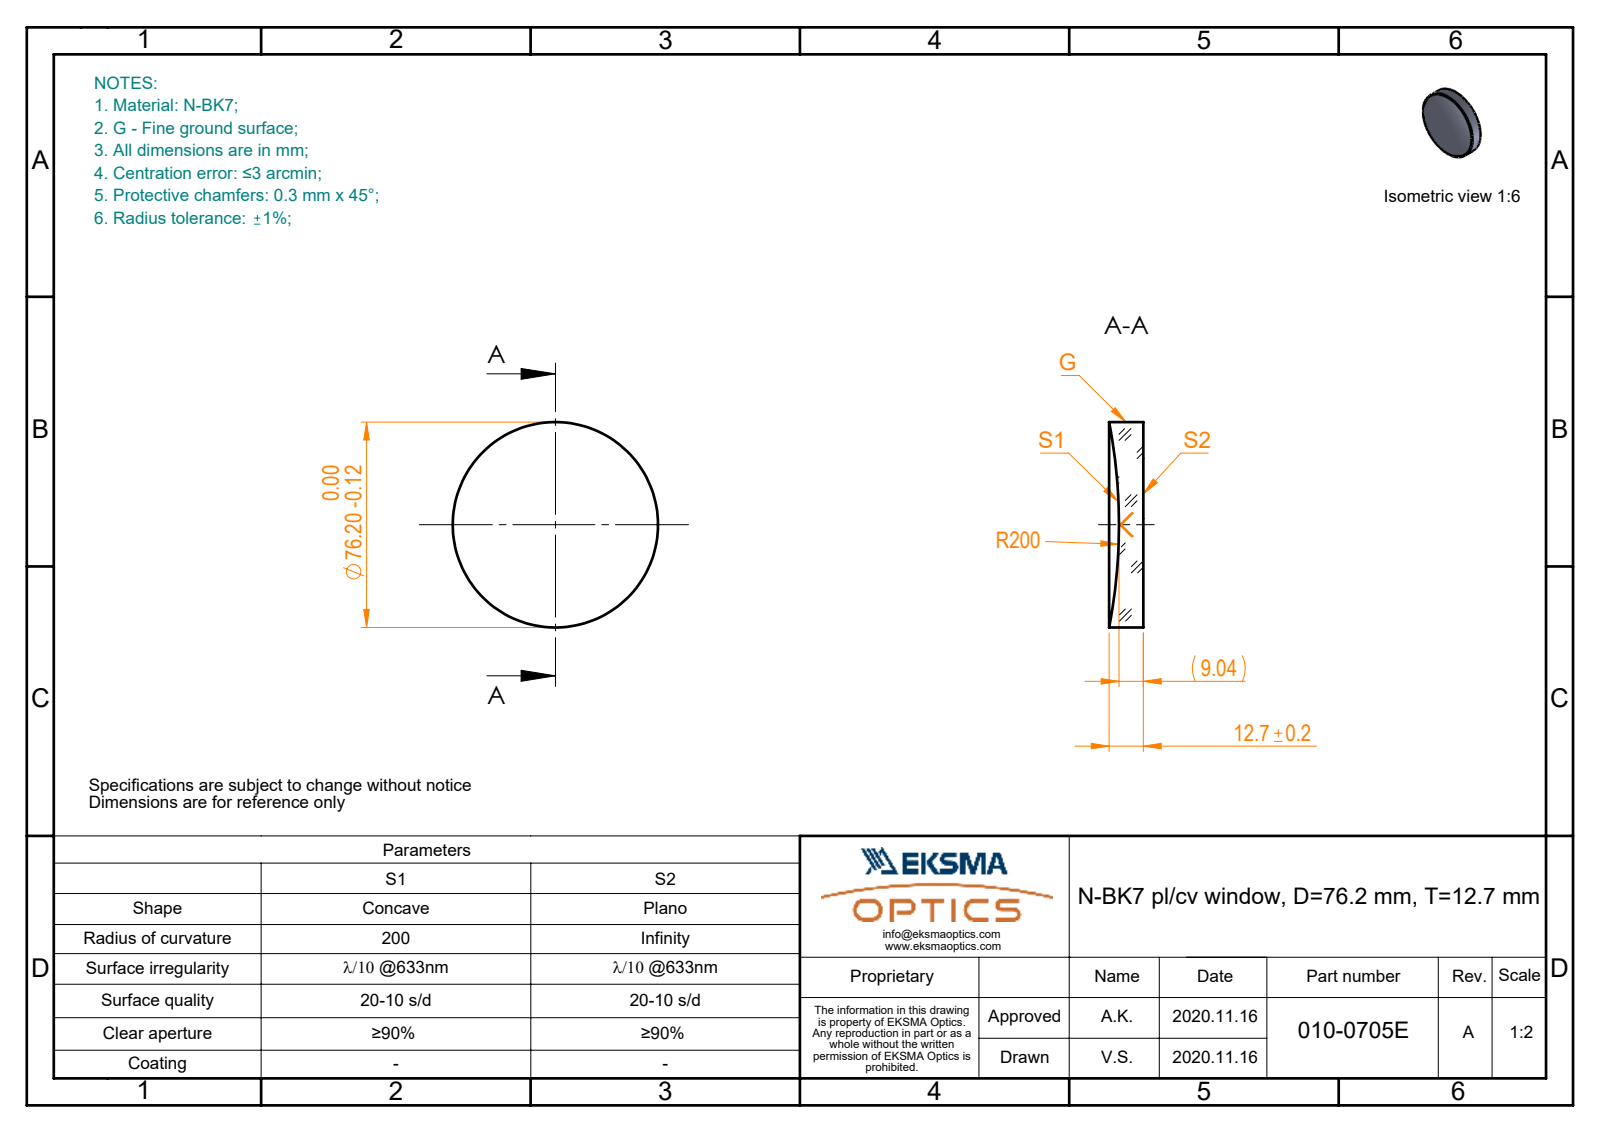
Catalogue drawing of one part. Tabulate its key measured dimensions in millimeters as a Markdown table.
| quantity | value |
| --- | --- |
| part name | 010-0705E_N-BK7_PCV_window |
| STEP written by | SolidWorks 2019 (CONFIG_CONTROL_DESIGN) |
| units | millimeters |
| bodies | 1 solid, 5 faces (1 planar, 2 cylindrical, 2 other) |
| overall size | 76.2 × 76.2 × 12.7 |
| volume | 49 540 mm³ |
| surface area | 12 203 mm² |
| round bosses / shafts (diameter × count) | 76.2 × 1 |
